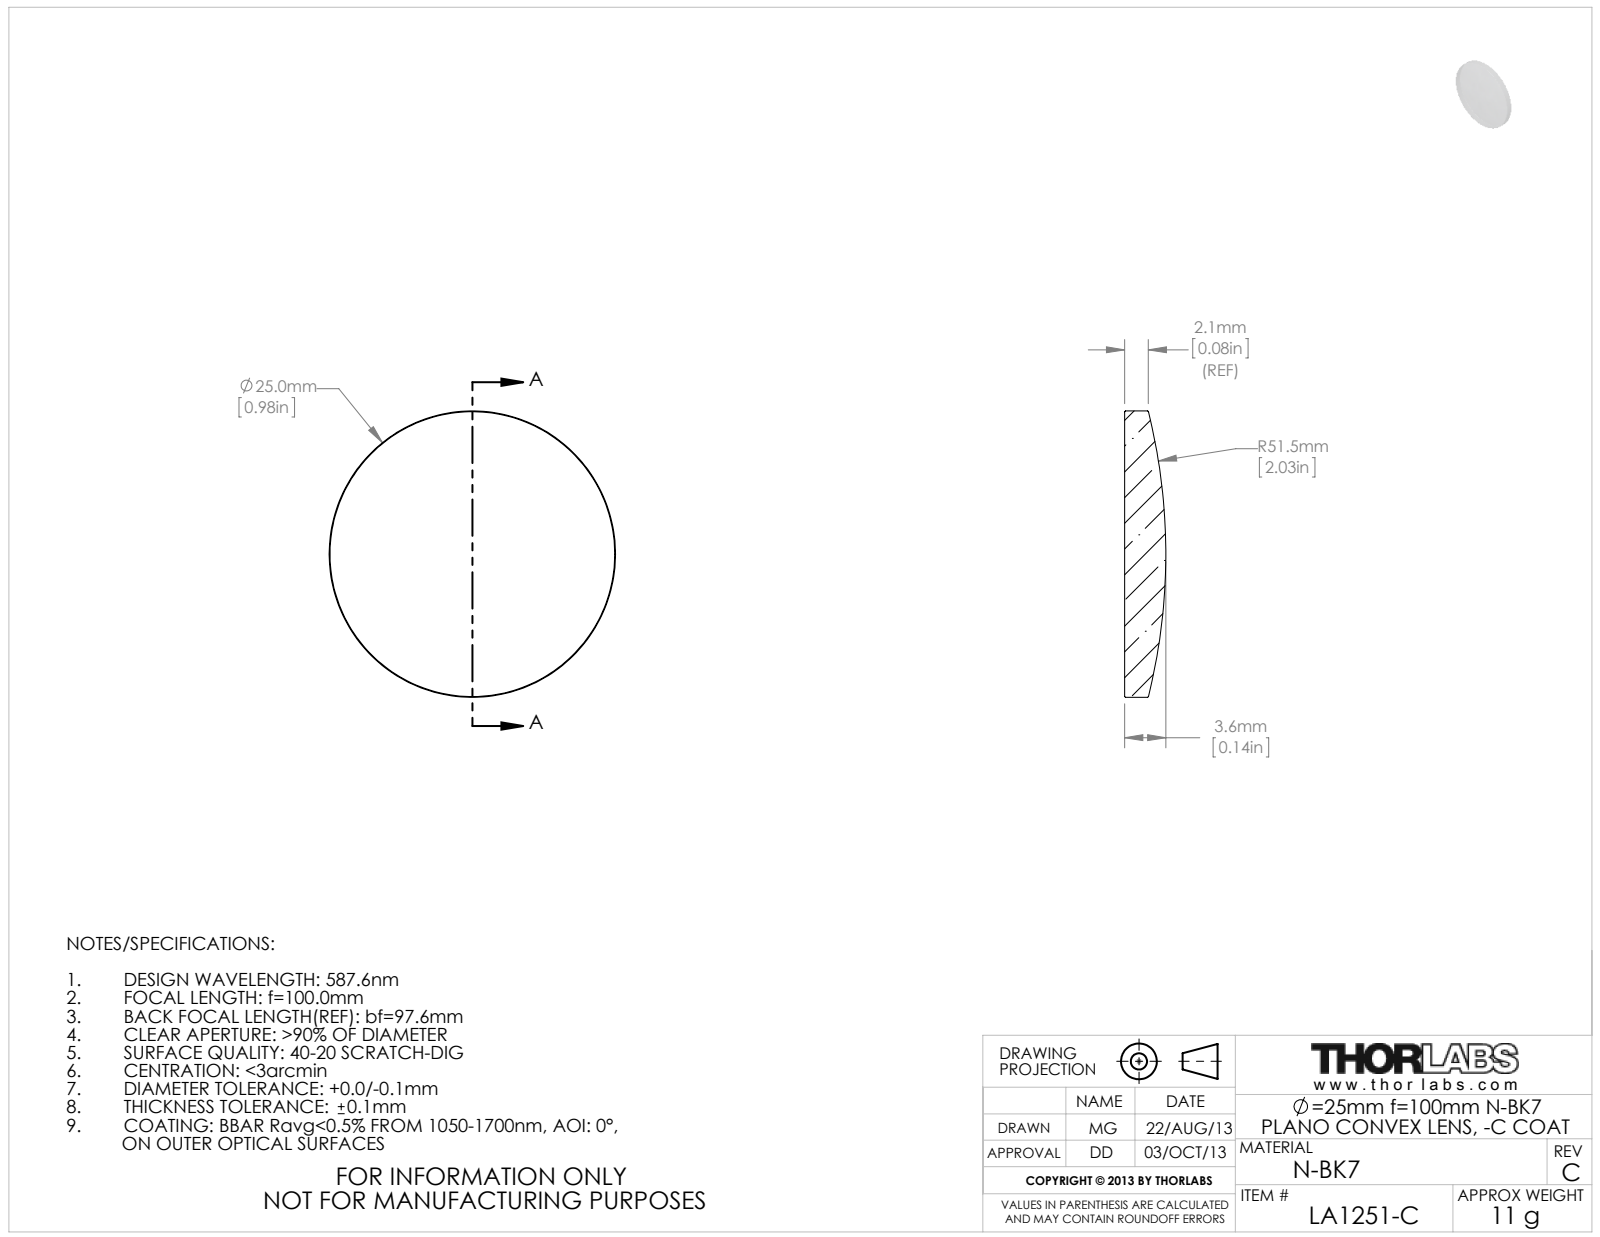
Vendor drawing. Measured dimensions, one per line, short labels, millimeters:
name: 19062-E0W
written by: SolidWorks 2009 (AUTOMOTIVE_DESIGN)
unit: mm
bodies: 1 solid, 5 faces (1 planar, 2 cylindrical, 2 other)
size: 25 × 25 × 3.6
volume: 1 391 mm³; area: 1 151 mm²
bosses: 1× ⌀25
